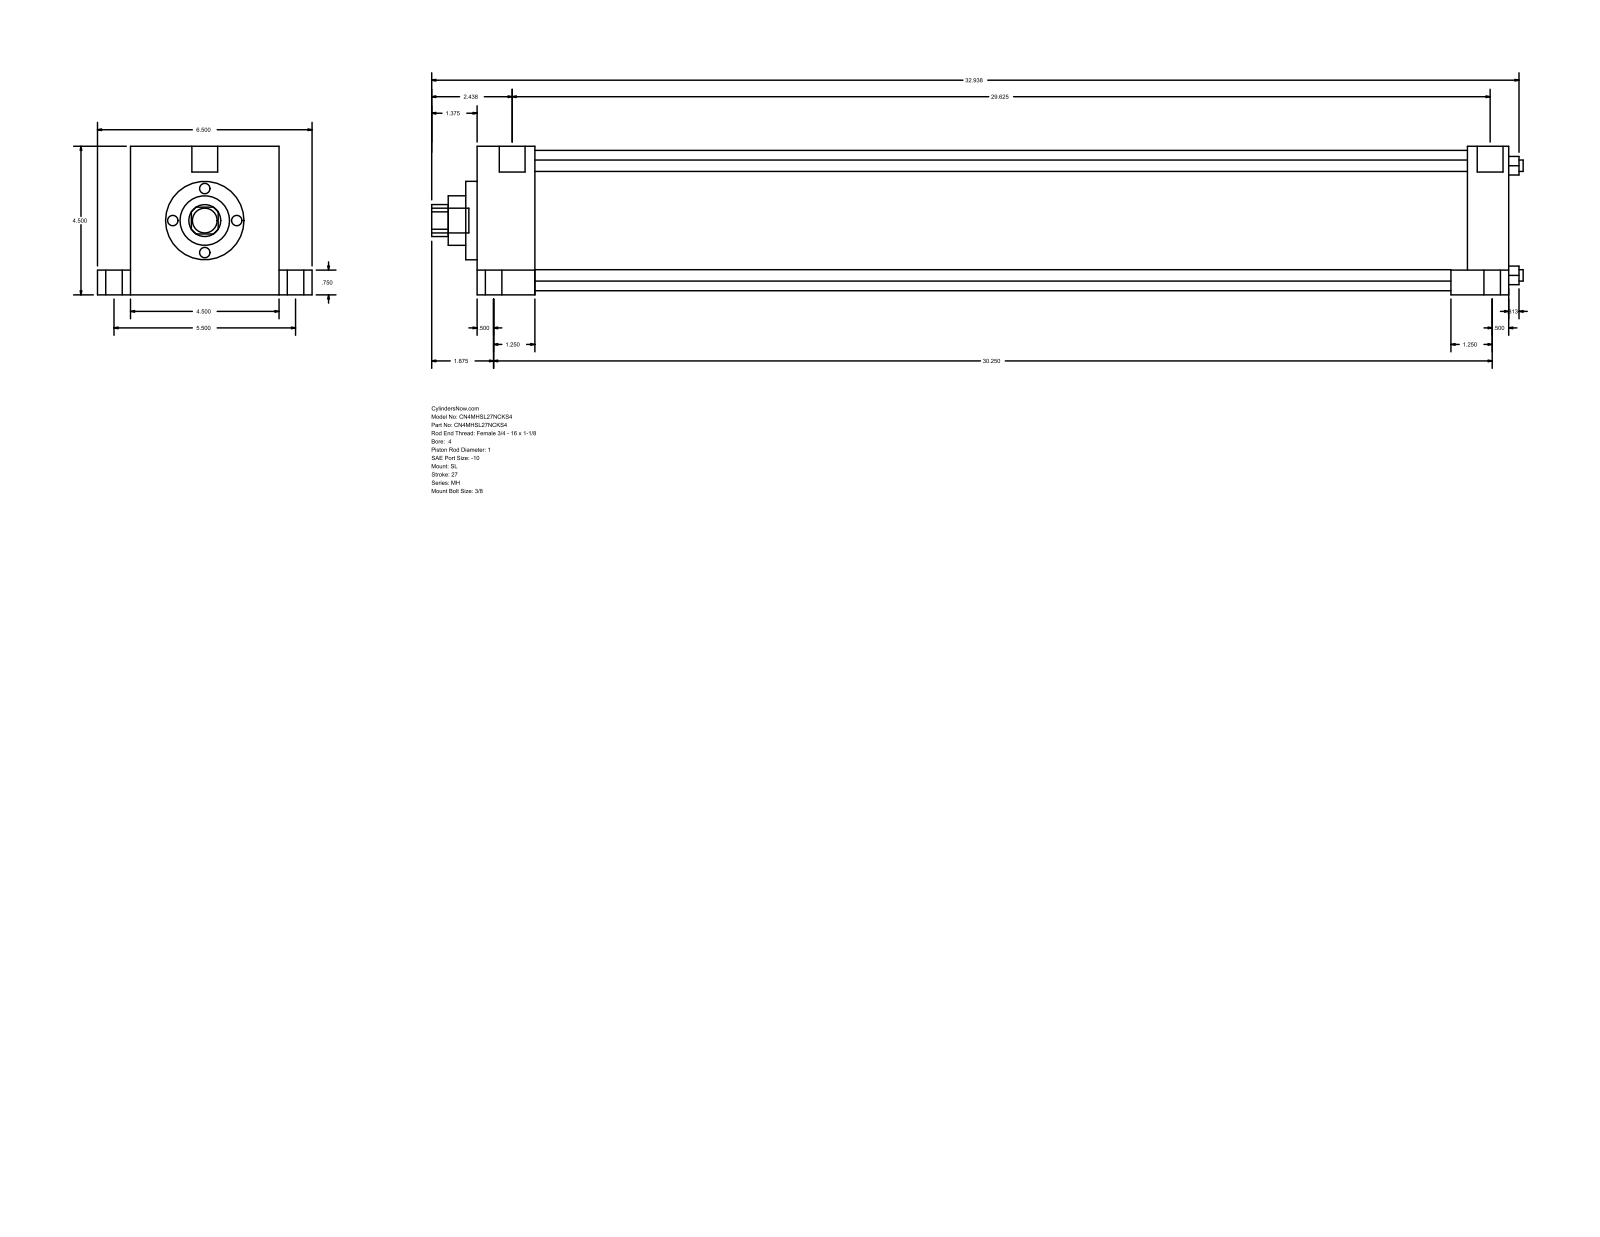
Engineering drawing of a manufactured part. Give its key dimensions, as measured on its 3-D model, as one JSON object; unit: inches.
{"part_name": "MH_SL__0400_1", "step_written_by": "GSSL Pune (CONFIG_CONTROL_DESIGN)", "units": "inches", "bodies": {"solids": 0, "faces": 110, "planar": 77, "cylindrical": 33, "other": 0}, "overall_size": [33.063, 6.5, 4.5], "round_holes": [[0.345, 4], [1, 1], [1.5, 1], [2.375, 1], [4.25, 1]], "round_bosses_or_shafts": [[0.75, 5], [0.5, 4], [0.344, 4], [0.781, 2]], "partial_cylinders_radius": [[0.484, 1]], "face_to_face_distances": [4.5, 31.25, 1.75, 29.5, 30, 28.25, 1.25, 1, 5.5, 0.75], "hole_center_spacings": [2.347, 3.32, 4.695]}
